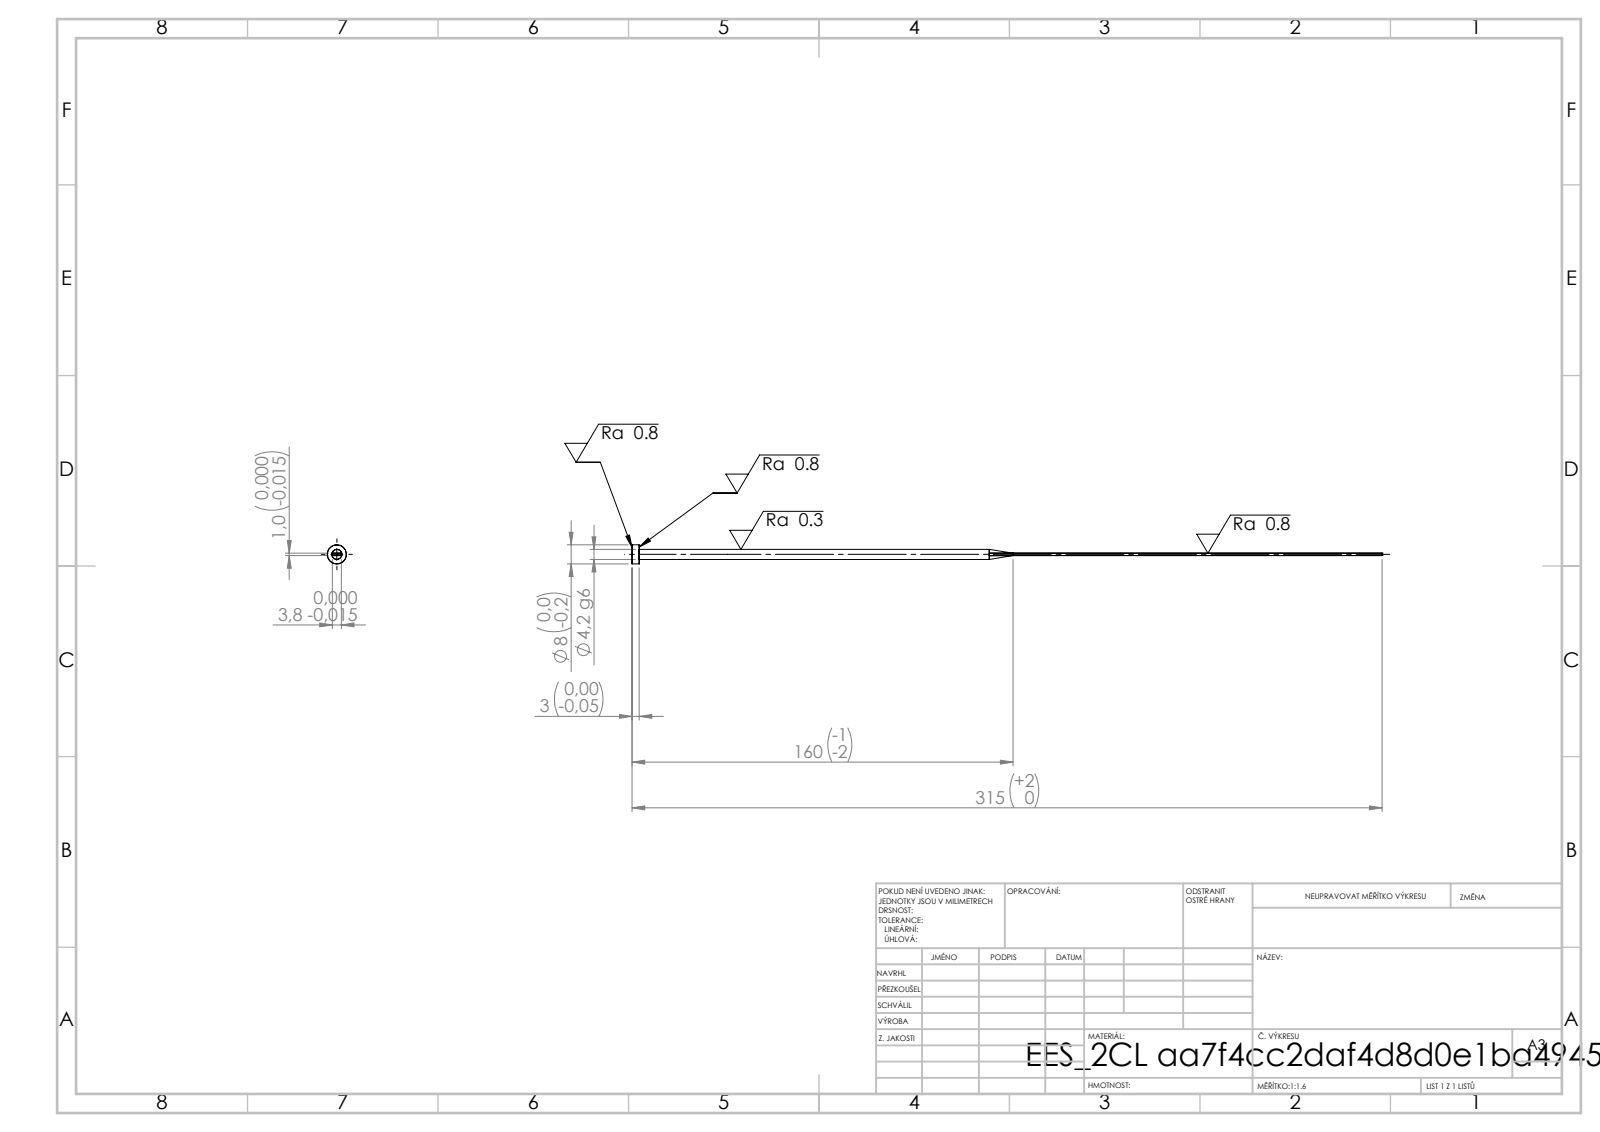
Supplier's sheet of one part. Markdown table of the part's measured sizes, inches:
| quantity | value |
| --- | --- |
| STEP written by | SolidWorks 2019 (CONFIG_CONTROL_DESIGN) |
| units | inches |
| bodies | 1 solid, 15 faces (7 planar, 4 cylindrical, 4 other) |
| overall size | 12.402 × 0.315 × 0.315 |
| volume | 0.175 in³ |
| surface area | 5.741 in² |
| round bosses / shafts (diameter × count) | 0.315 × 1, 0.165 × 1 |
| main face-to-face distances | 0.039, 0.15, 0.118, 12.402, 12.283 |
